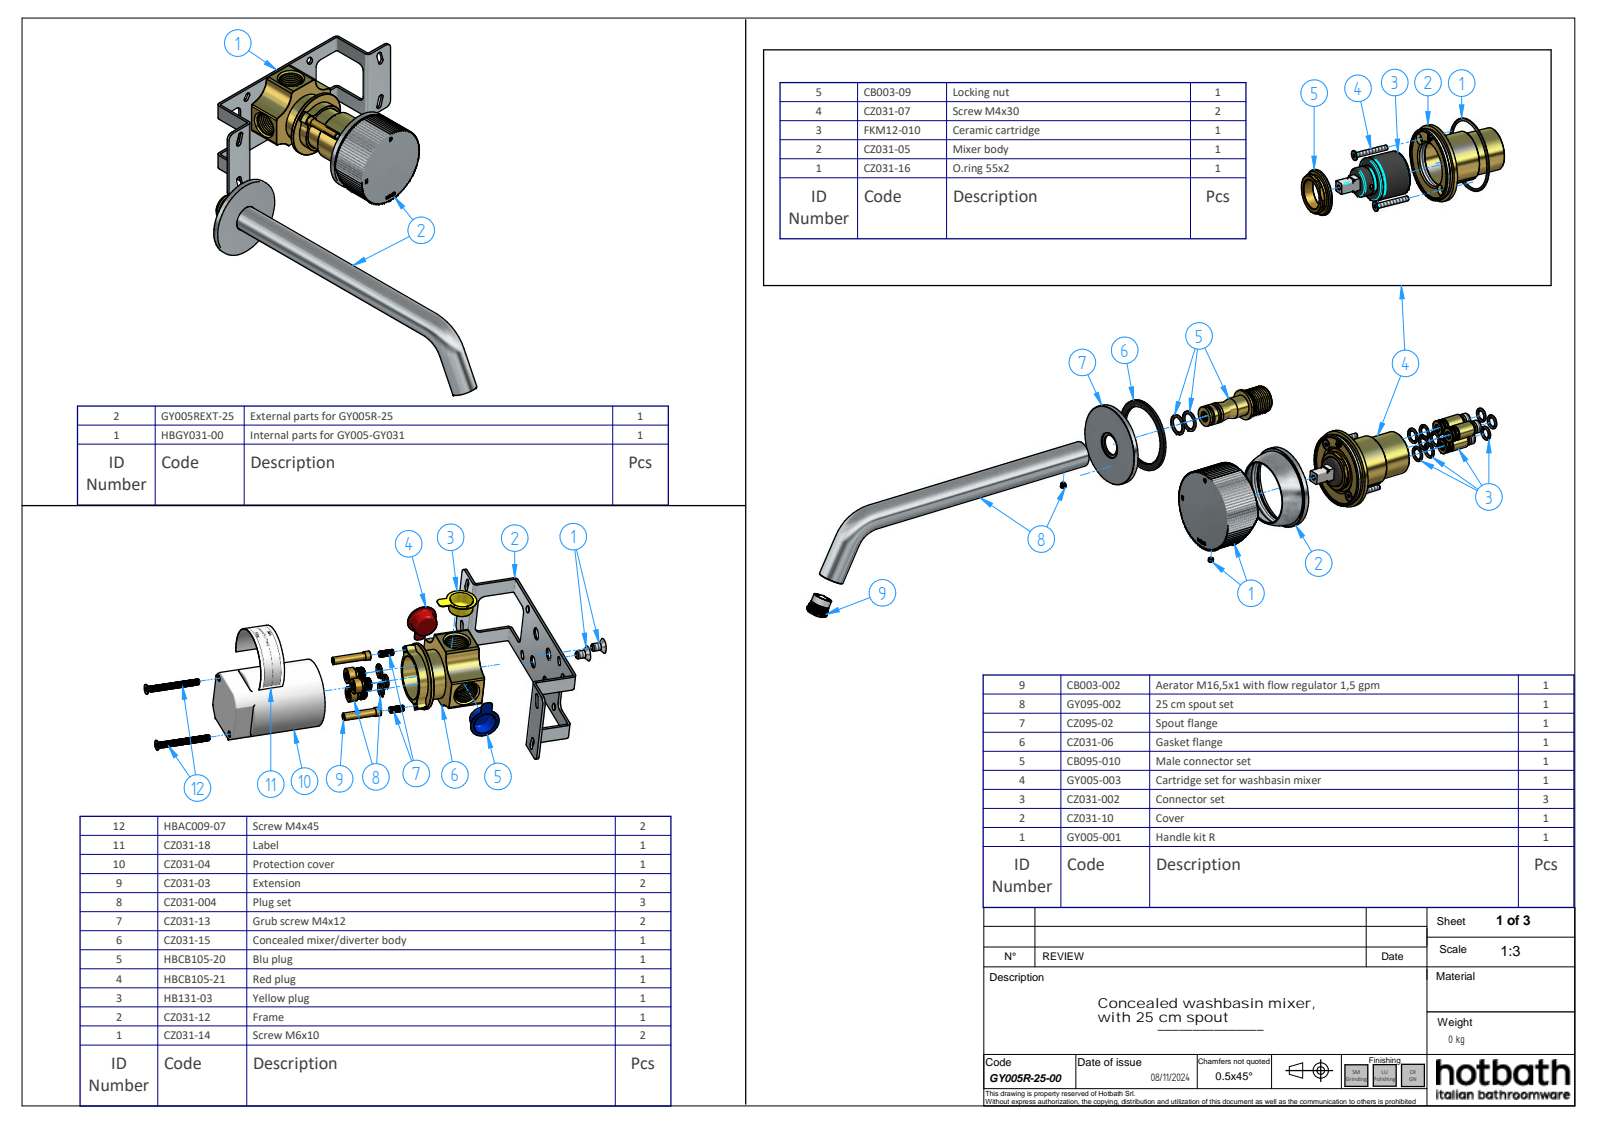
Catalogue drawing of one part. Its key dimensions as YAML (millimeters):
part_name: "GY005REXT25-00; GY005-001_oa_0; GY005-01; GY095-25-00_oa_1 (+8 more)"
step_written_by: "Solid Edge (AUTOMOTIVE_DESIGN)"
units: millimeters
bodies: {solids: 9, faces: 1914, planar: 348, cylindrical: 595, other: 971}
overall_size: [5155.02, 5057.82, 5057.82]
volume: 68280000000
surface_area: 80850000
round_holes:
  - {diameter: 16, count: 2}
  - {diameter: 3.24, count: 1}
  - {diameter: 3.3, count: 1}
  - {diameter: 4, count: 1}
  - {diameter: 4.5, count: 1}
  - {diameter: 11, count: 1}
  - {diameter: 11.03, count: 1}
  - {diameter: 12.2, count: 1}
  - {diameter: 14.58, count: 1}
  - {diameter: 16.1, count: 1}
  - {diameter: 16.3, count: 1}
  - {diameter: 16.75, count: 1}
round_bosses_or_shafts:
  - {diameter: 64, count: 2}
  - {diameter: 20, count: 2}
  - {diameter: 29, count: 1}
  - {diameter: 16.5, count: 1}
  - {diameter: 16, count: 1}
  - {diameter: 15.42, count: 1}
  - {diameter: 15.23, count: 1}
  - {diameter: 15.22, count: 1}
partial_cylinders:
  - {radius: 0.2, count: 361}
  - {radius: 0.1, count: 90}
  - {radius: 0.49, count: 1}
face_to_face_distances: [28.5, 2.3, 30.8, 1, 4, 1.7, 32.5, 1.2, 3, 1.3]
hole_center_spacings: [130, 130.08, 130.15]
